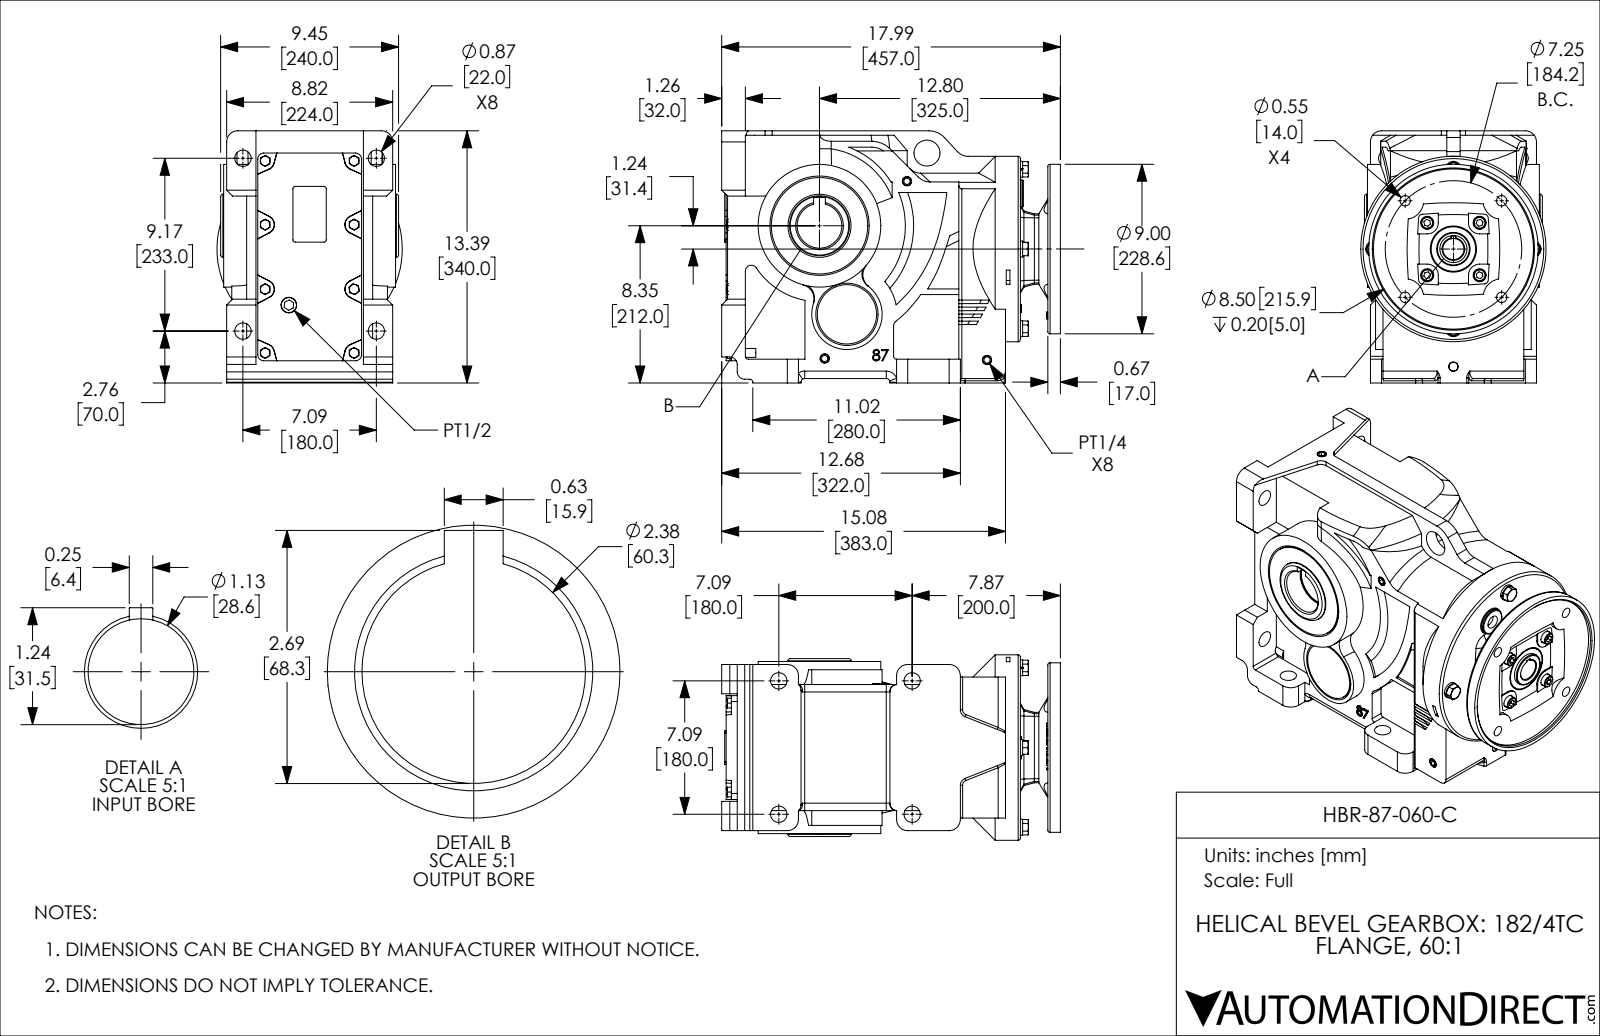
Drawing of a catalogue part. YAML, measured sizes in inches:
part_name: "HBR-87-060-C"
step_written_by: "SolidWorks 2018 (AUTOMOTIVE_DESIGN)"
units: inches
bodies: {solids: 8, faces: 1111, planar: 542, cylindrical: 287, other: 282}
overall_size: [17.992, 13.501, 9.843]
volume: 1396
surface_area: 1309
round_holes:
  - {diameter: 0.551, count: 8}
  - {diameter: 0.866, count: 8}
  - {diameter: 0.48, count: 4}
  - {diameter: 0.496, count: 4}
  - {diameter: 0.689, count: 4}
  - {diameter: 0.473, count: 1}
  - {diameter: 0.709, count: 1}
  - {diameter: 0.827, count: 1}
  - {diameter: 1.125, count: 1}
  - {diameter: 1.378, count: 1}
  - {diameter: 1.417, count: 1}
  - {diameter: 2.375, count: 1}
round_bosses_or_shafts:
  - {diameter: 0.846, count: 4}
  - {diameter: 0.63, count: 4}
  - {diameter: 0.472, count: 4}
  - {diameter: 9.843, count: 1}
  - {diameter: 9, count: 1}
  - {diameter: 6.513, count: 1}
  - {diameter: 5.118, count: 1}
  - {diameter: 3.346, count: 1}
partial_cylinders:
  - {radius: 0.394, count: 15}
  - {radius: 0.591, count: 14}
  - {radius: 0.157, count: 11}
  - {radius: 0.118, count: 9}
  - {radius: 0.315, count: 6}
  - {radius: 0.689, count: 4}
  - {radius: 0.984, count: 4}
  - {radius: 19.528, count: 4}
face_to_face_distances: [0.669, 0.236, 6.024, 1.063, 1.457, 7.087, 13.15, 0.394, 15.63, 1.22]
hole_center_spacings: [3.163, 7.087, 7.263, 2.784, 3.059, 4.125, 4.125, 4.232]
